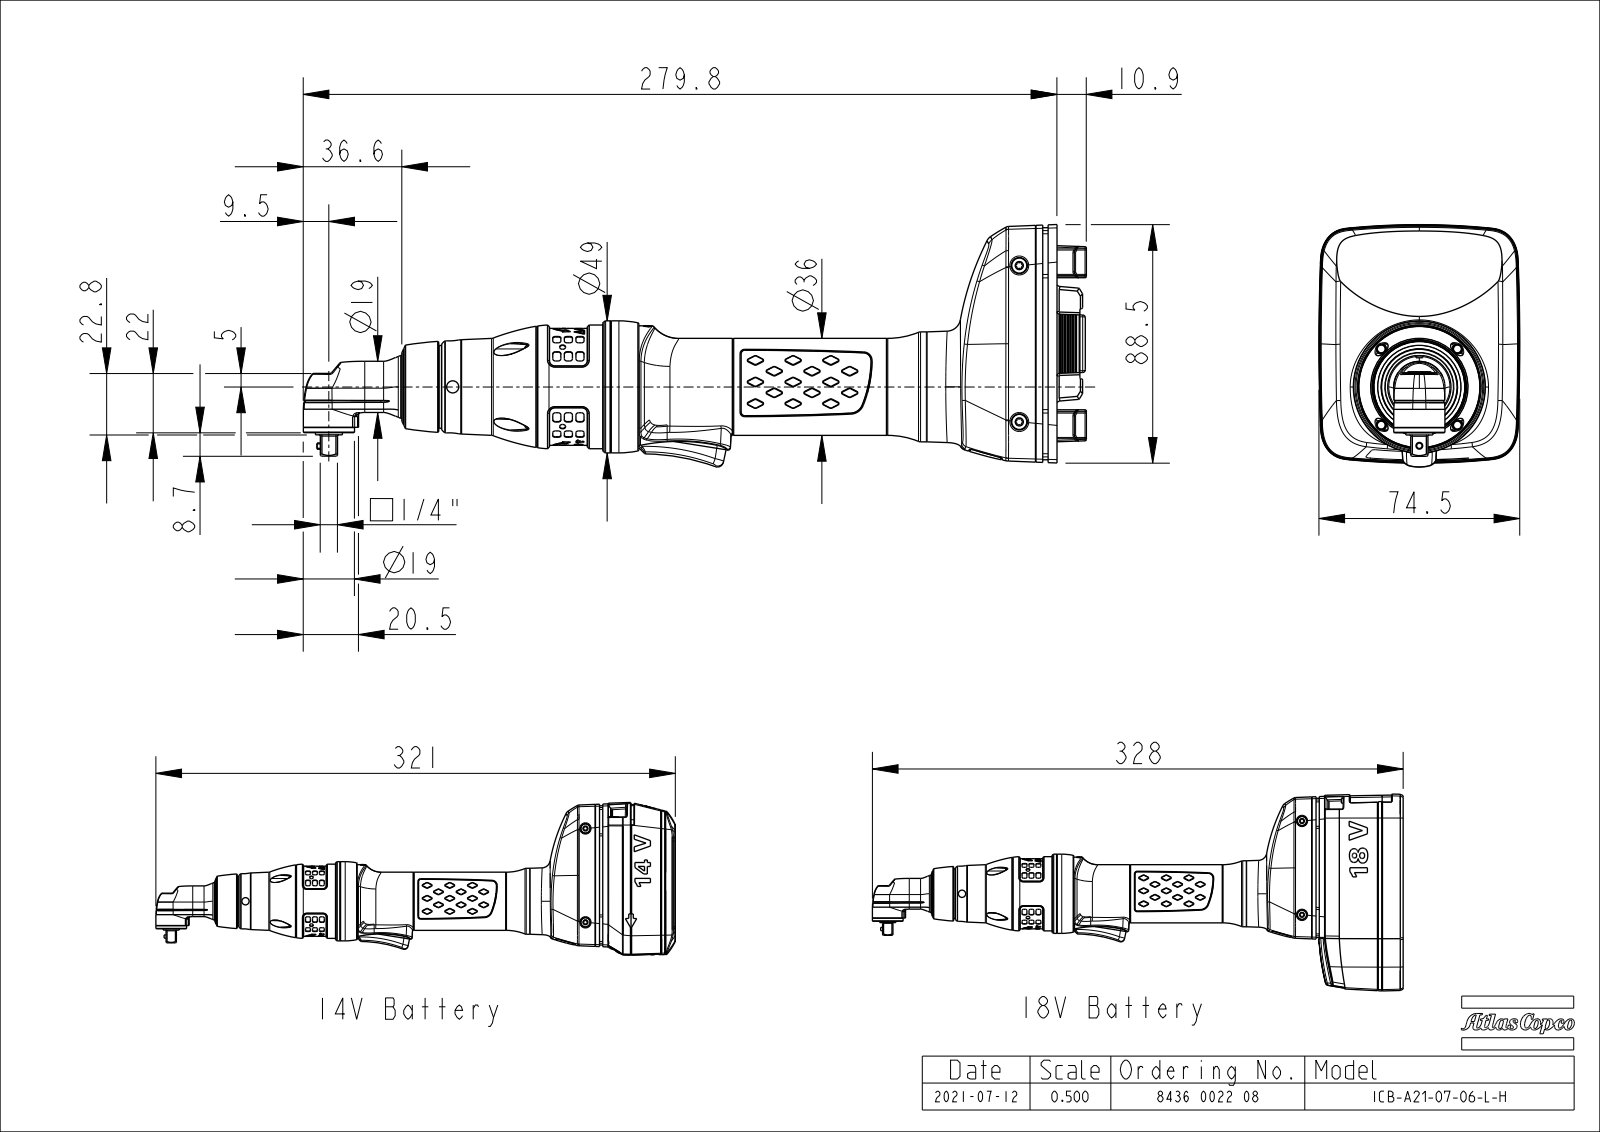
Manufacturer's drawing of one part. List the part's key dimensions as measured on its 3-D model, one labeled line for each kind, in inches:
Part name (STEP PRODUCT): EXT_COMP_SW0007
STEP written by: CREO PARAMETRIC BY PTC INC, 2020281 (CONFIG_CONTROL_DESIGN)
Units: inches
Bodies: 1 solid, 2991 faces (893 planar, 626 cylindrical, 1472 other)
Overall size (bounding box): 11.402 × 3.543 × 2.935
Volume: 28.48 in³ · Surface area: 96.97 in²
Round holes (diameter × count): ⌀0.102 ×4, ⌀0.098 ×2, ⌀0.177 ×2, ⌀0.236 ×2, ⌀0.043 ×1, ⌀0.063 ×1, ⌀0.114 ×1, ⌀0.138 ×1, ⌀0.402 ×1, ⌀0.906 ×1
Round bosses / shafts (diameter × count): ⌀0.315 ×4, ⌀0.115 ×4, ⌀0.22 ×2, ⌀1.929 ×1, ⌀1.807 ×1, ⌀1.783 ×1, ⌀1.709 ×1, ⌀1.606 ×1
Partial cylindrical surfaces — rounded edges, fillets, slot ends (radius × count): R0.02 ×90, R0.039 ×67, R0.011 ×24, R0.015 ×24, R0.02 ×24, R0.027 ×24, R0.008 ×12, R0.012 ×12
Main face-to-face distances: 0.413, 0.331, 2.362, 0.421, 0.419, 0.039, 0.543, 0.13, 0.122, 0.266
Hole centre spacings: 0.289, 0.409, 0.579, 0.858, 1.469, 1.758, 1.78, 1.783
